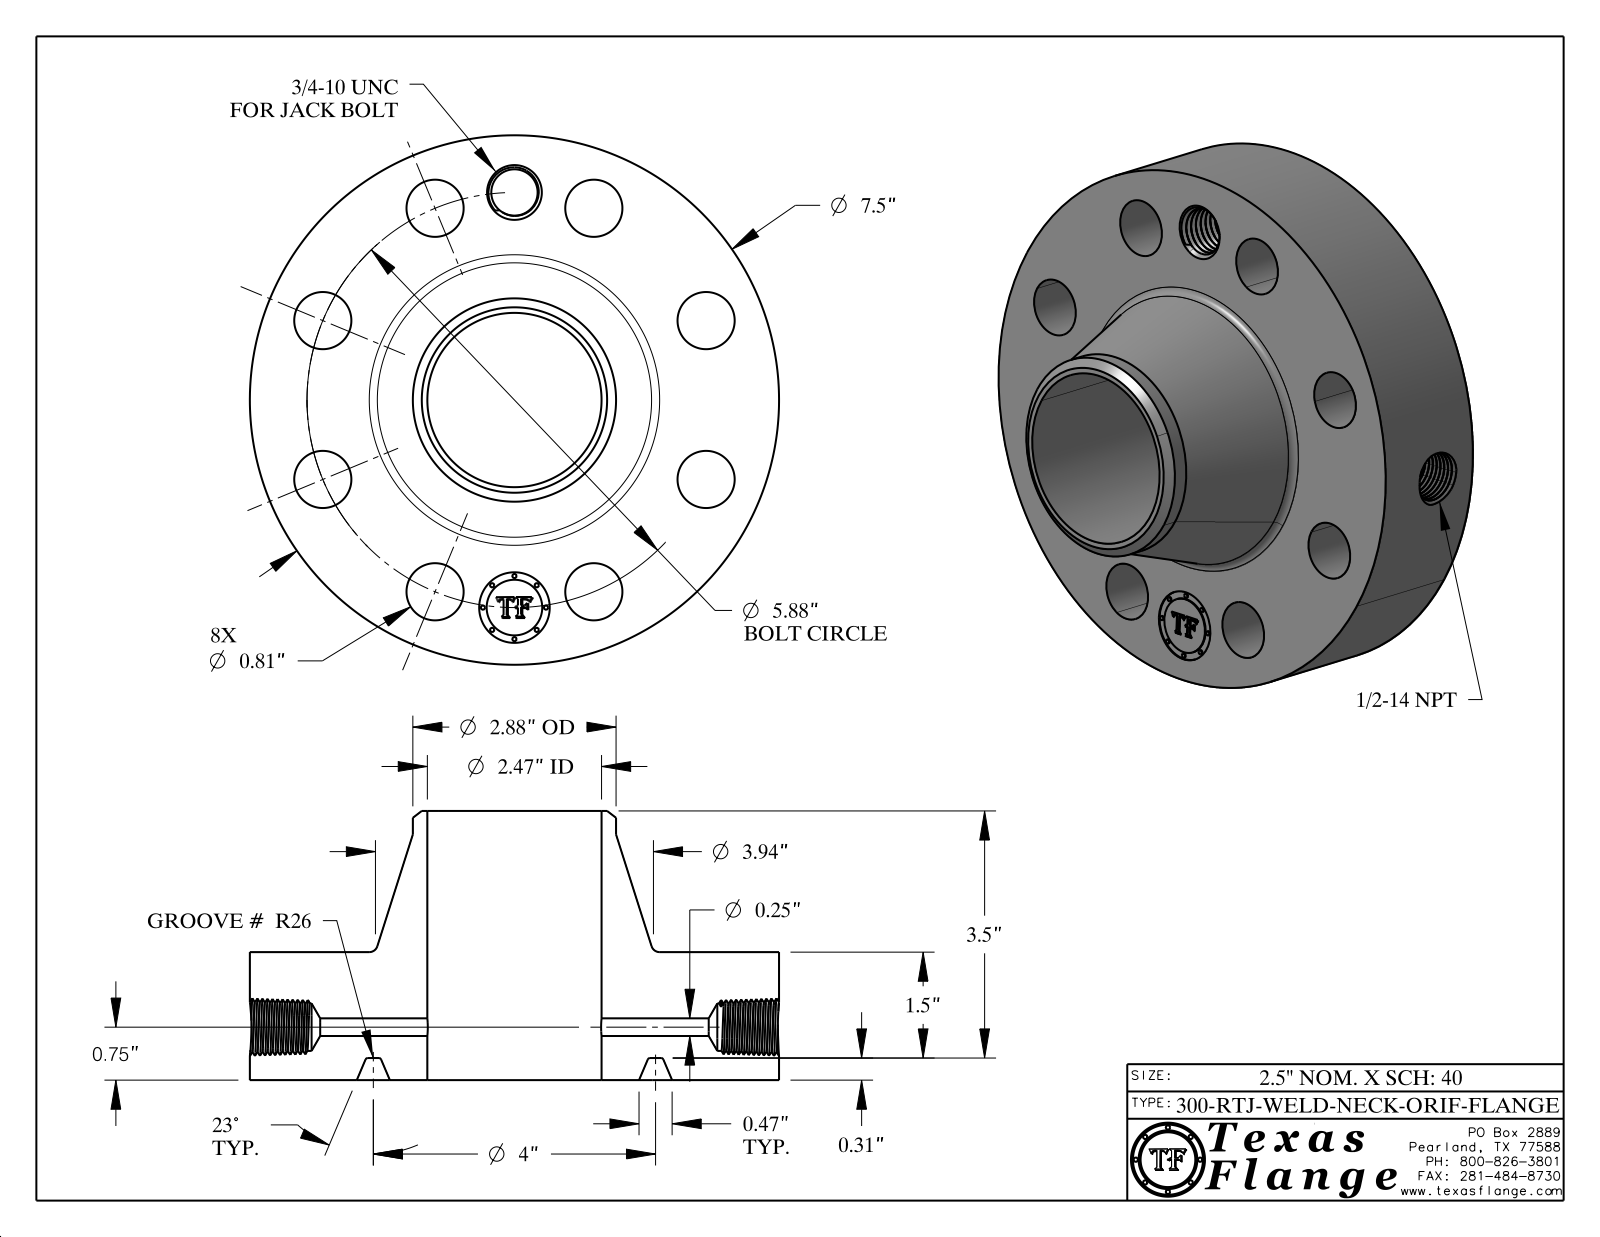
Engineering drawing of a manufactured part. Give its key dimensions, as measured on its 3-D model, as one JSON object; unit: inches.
{"part_name": "300-RTJ-WELD-NECK", "step_written_by": "CATIA V5 STEP AP214 (AUTOMOTIVE_DESIGN)", "units": "inches", "bodies": {"solids": 1, "faces": 797, "planar": 370, "cylindrical": 96, "other": 331}, "overall_size": [7.5, 7.5, 3.813], "volume_in3": 68.88, "surface_area_in2": 214.1, "round_holes": [[0.81, 8], [0.25, 1], [0.656, 1], [0.672, 1], [1, 1], [2.469, 1]], "round_bosses_or_shafts": [[0.061, 8], [7.5, 1], [2.88, 1], [0.788, 1]], "face_to_face_distances": [1.813, 0.313, 1.5, 3.813, 3.5, 2, 0.015, 1.798, 1.485, 2.015], "hole_center_spacings": [2.94, 4.158, 5.432, 1.147, 2.25, 2.25, 3.267, 4.889]}
